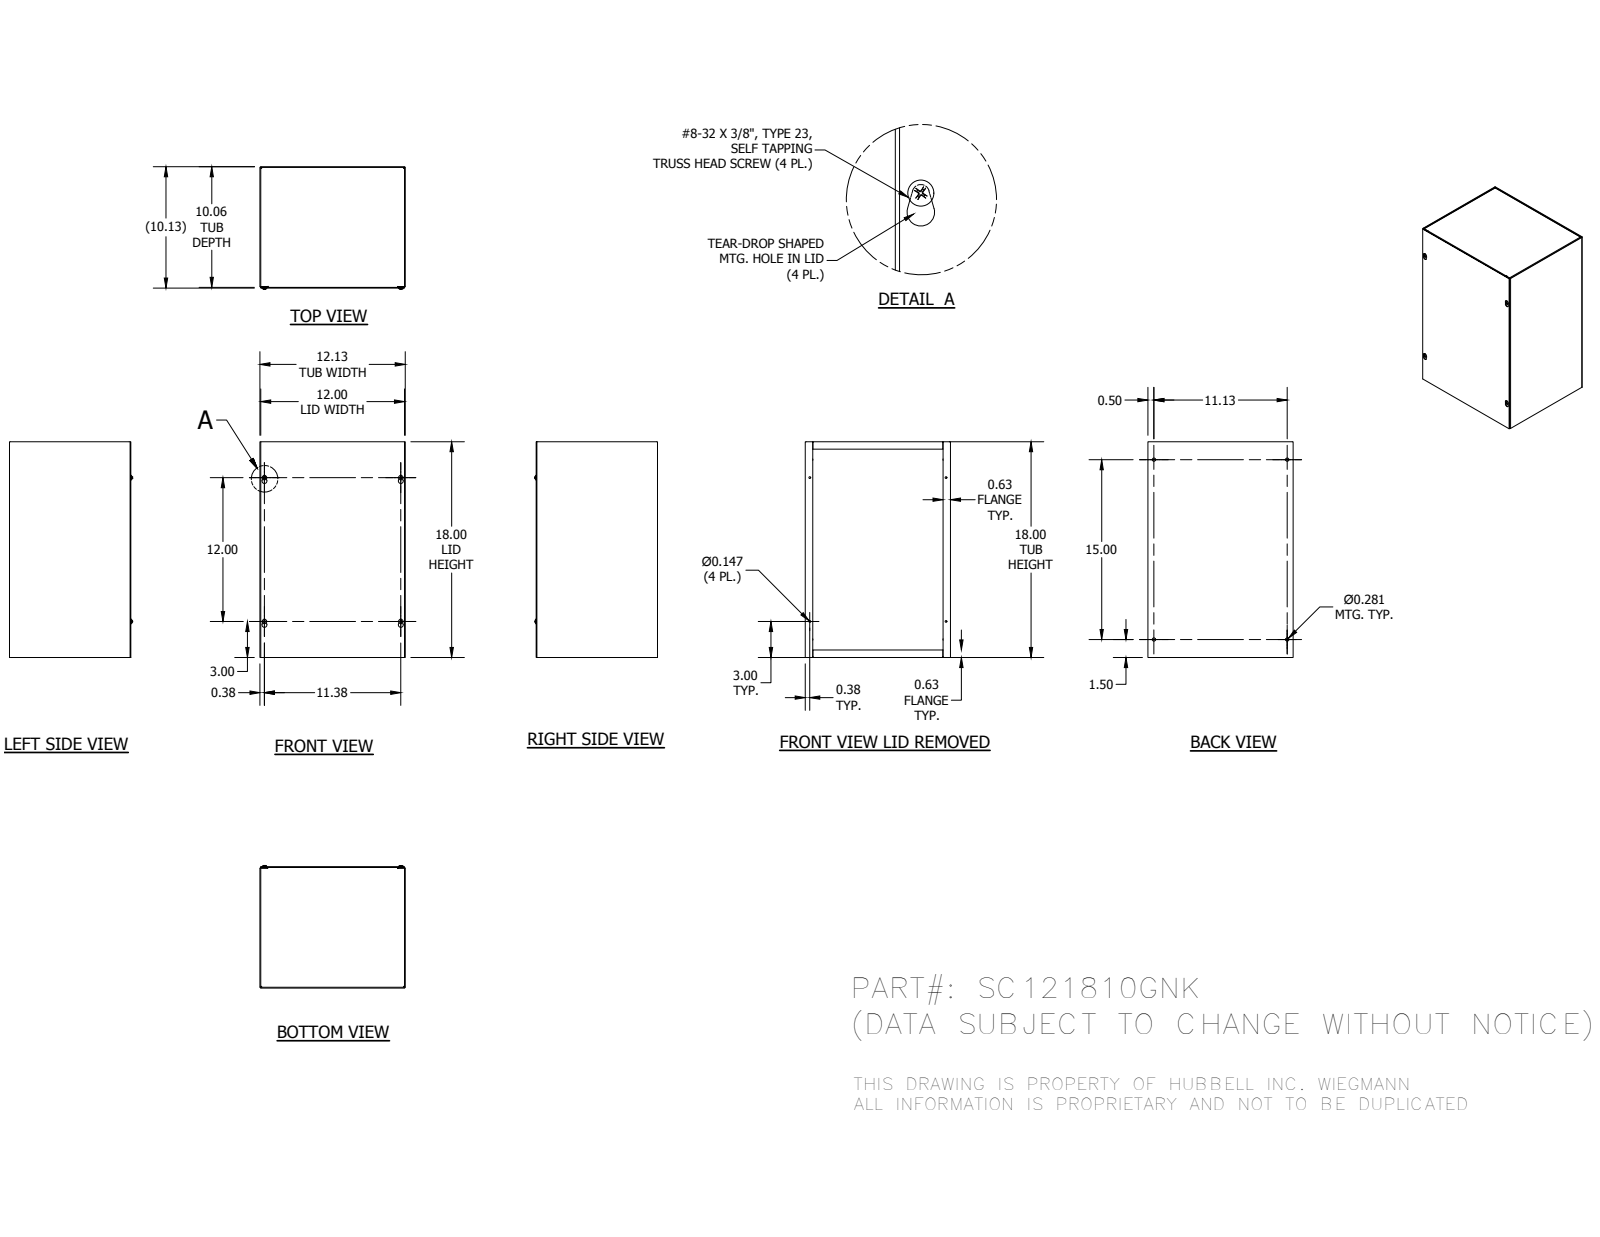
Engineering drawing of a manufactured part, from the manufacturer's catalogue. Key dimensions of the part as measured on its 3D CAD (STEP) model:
Part name (STEP PRODUCT): SC121810GNKBLR; SC1210GNKTB; SC1218GLPA; 34056 (+1 more)
STEP written by: Autodesk Inventor 2014 (AUTOMOTIVE_DESIGN)
Units: millimetres
Bodies: 8 solids, 268 faces (152 planar, 48 cylindrical, 68 other)
Overall size (bounding box): 457.2 × 307.98 × 259.72
Volume: 1 125 000 mm³ · Surface area: 1 429 000 mm²
Round holes (diameter × count): ⌀3.73 ×4, ⌀7.14 ×4
Round bosses / shafts (diameter × count): ⌀9.75 ×4, ⌀4.17 ×4
Partial cylindrical surfaces — rounded edges, fillets, slot ends (radius × count): R0.4 ×12, R1.98 ×12, R3.17 ×4, R5.16 ×4
Main face-to-face distances: 1.59, 306.39, 254, 455.61, 1.58, 255.59, 255.58, 257.17, 304.8, 307.98
Hole centre spacings: 38.23, 288.28, 342.91, 446.36, 282.58, 288.92, 304.8, 381
